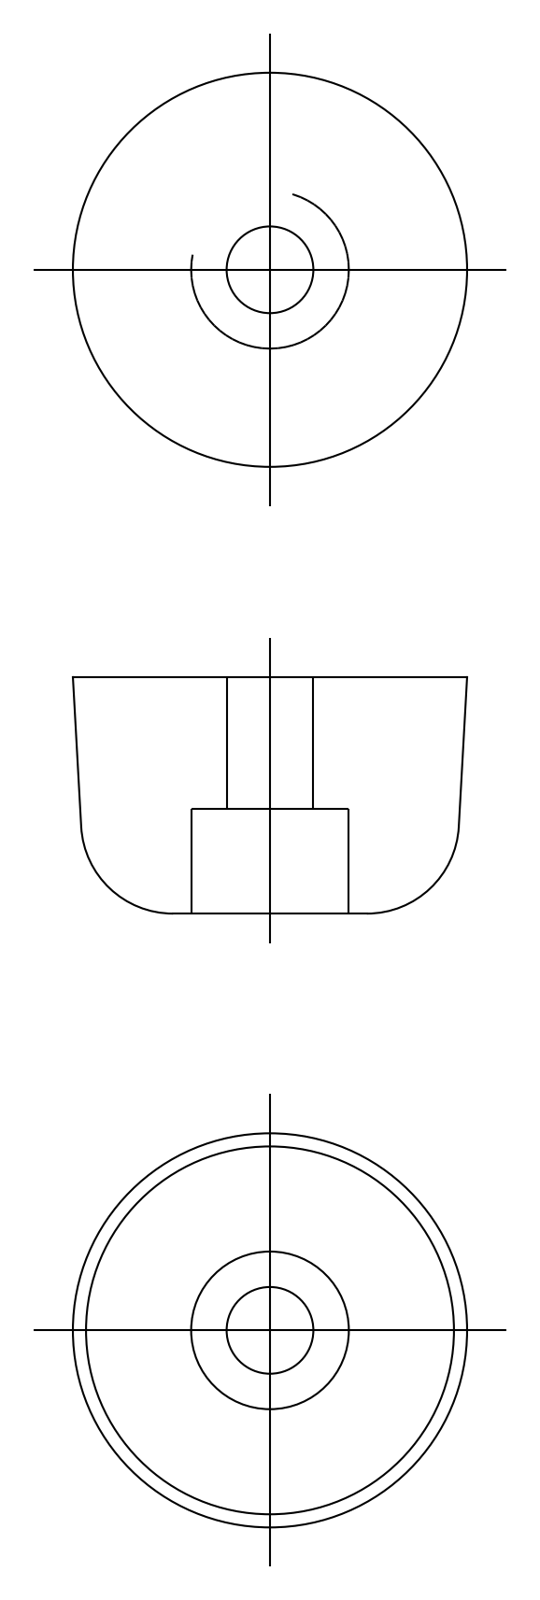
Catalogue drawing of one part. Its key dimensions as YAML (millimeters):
step_written_by: "spGate 19.8.4 (****-****-****-****) (AUTOMOTIVE_DESIGN)"
units: millimeters
bodies: {solids: 1, faces: 11, planar: 3, cylindrical: 4, other: 4}
overall_size: [15, 15, 9]
volume: 1242
surface_area: 789
round_holes:
  - {diameter: 3.3, count: 1}
  - {diameter: 6, count: 1}
face_to_face_distances: [5, 4, 9]
